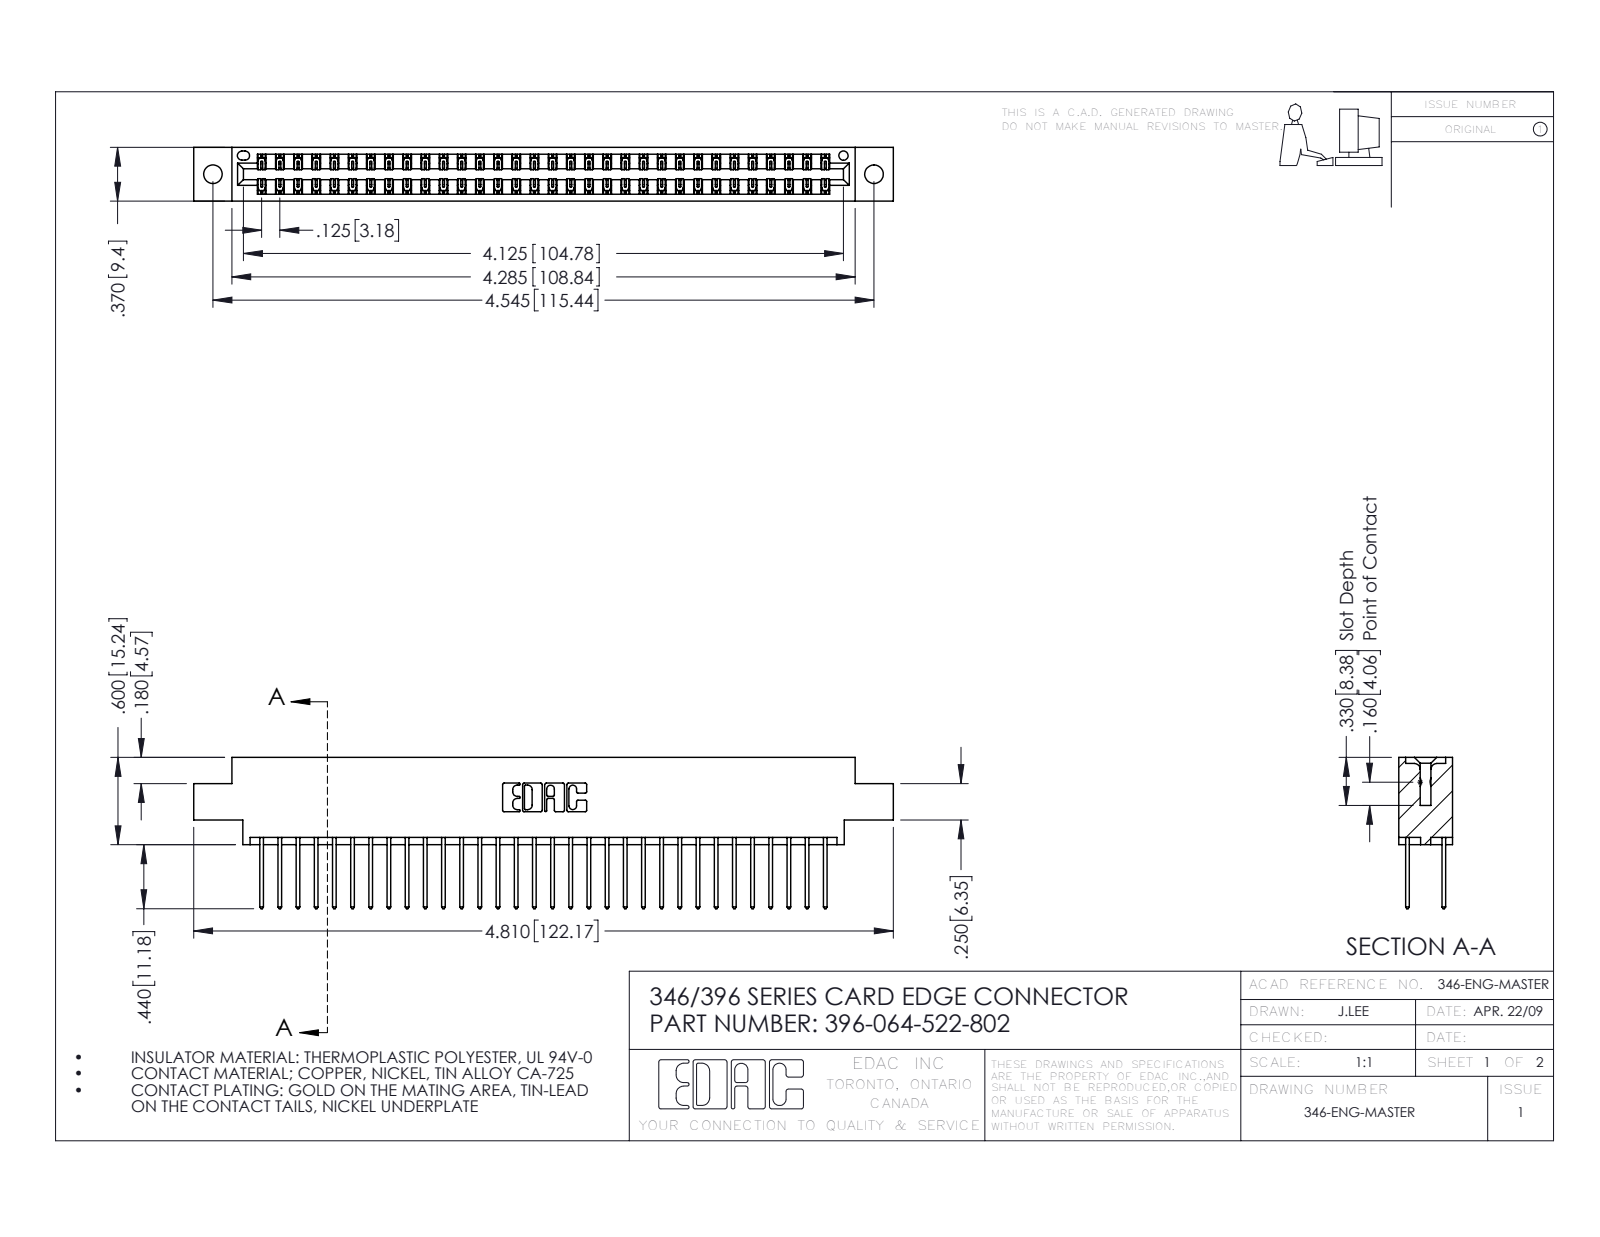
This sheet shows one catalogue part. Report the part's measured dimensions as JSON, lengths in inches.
{"part_name": "396-064-522-802; 346 Part_0.170 Offset - 0.128 Dia; 345-292-001_345-293-122", "step_written_by": "SolidWorks 2016 (CONFIG_CONTROL_DESIGN)", "units": "inches", "bodies": {"solids": 65, "faces": 3454, "planar": 2320, "cylindrical": 1134, "other": 0}, "overall_size": [4.81, 1.04, 0.37], "volume_in3": 0.721, "surface_area_in2": 25.95, "round_holes": [[0.128, 2], [0.064, 1]], "partial_cylinders_radius": [[0.006, 96], [0.01, 64], [0.01, 22], [0.007, 6], [0.031, 6], [0.026, 3], [0.014, 2], [0.022, 2]], "face_to_face_distances": [0.048, 0.322, 0.25, 0.37, 0.072, 0.298, 0.025, 0.275, 0.148, 0.222], "hole_center_spacings": [0.246, 4.337, 4.545]}
